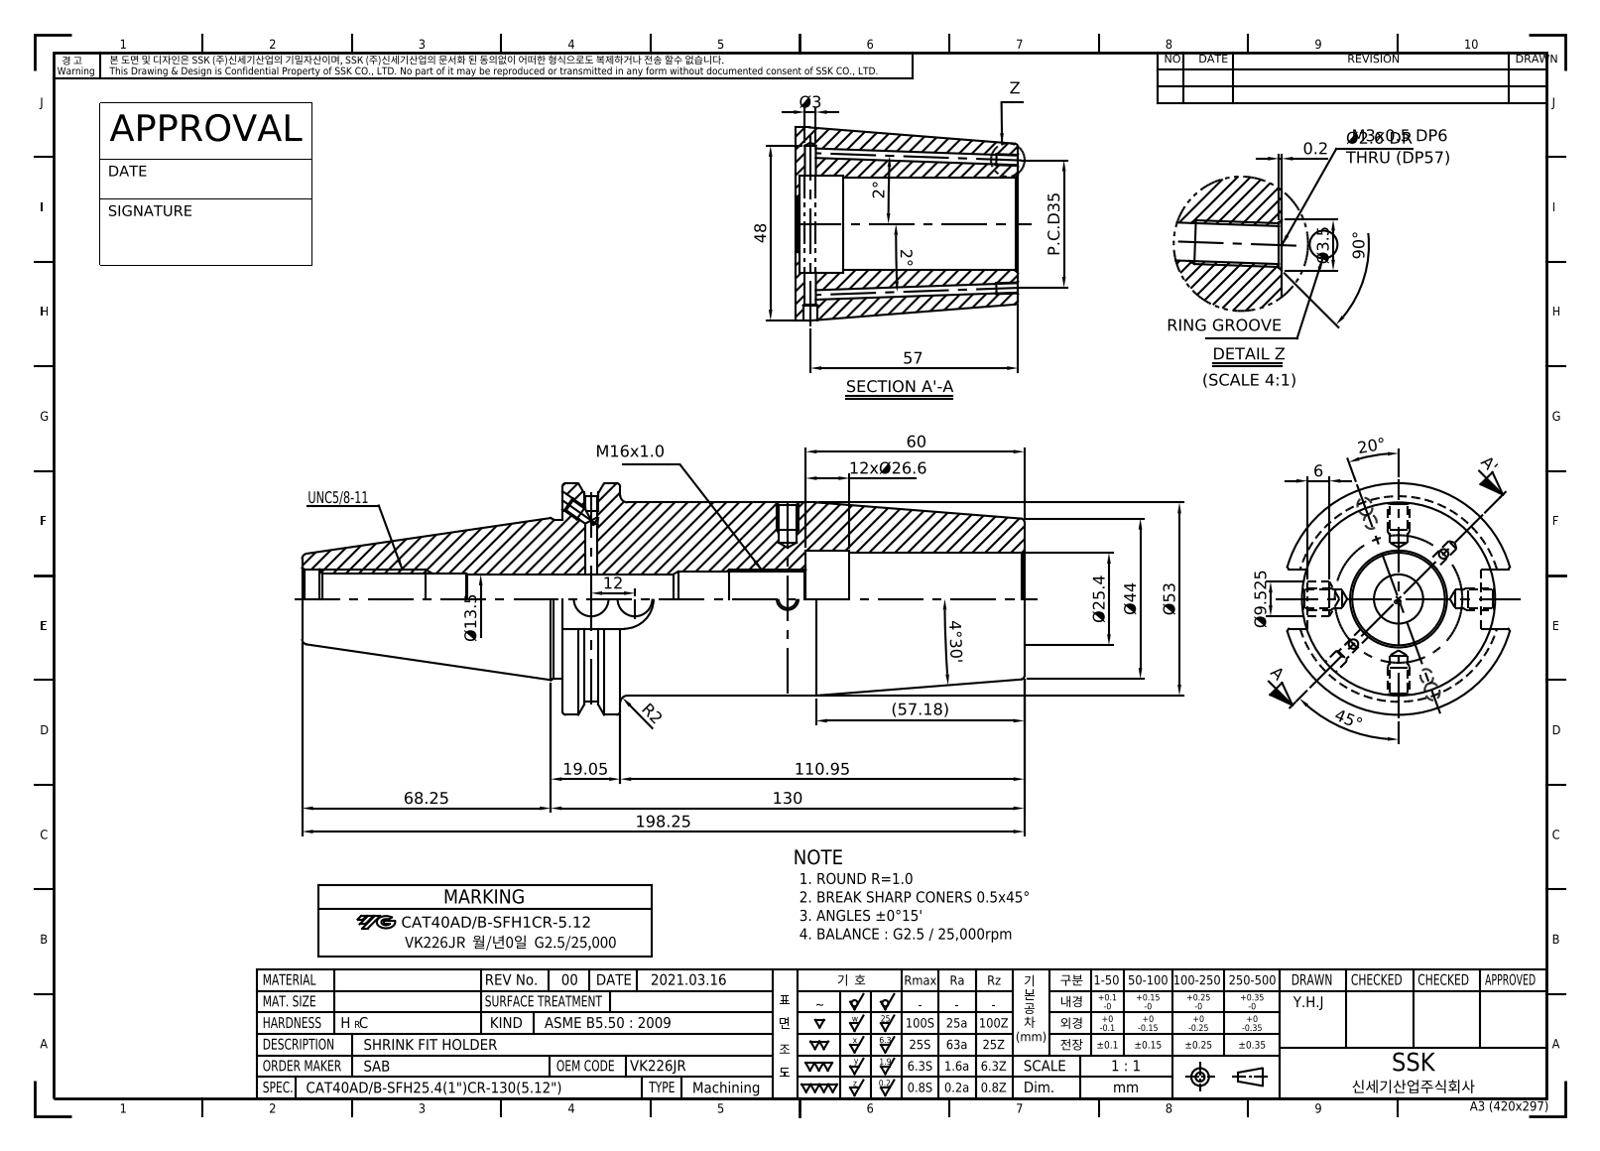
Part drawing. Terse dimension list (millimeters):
name: LO-CAT40ADB-SFH25.4CR-130
written by: Autodesk Inventor 2022 (AUTOMOTIVE_DESIGN)
unit: mm
bodies: 1 solid, 91 faces (34 planar, 33 cylindrical, 24 other)
size: 198.25 × 63.5 × 61.09
volume: 284 993 mm³; area: 45 781 mm²
holes: 4× ⌀3.24, 2× ⌀2.46, 2× ⌀4, 2× ⌀4.2, 1× ⌀9.53, 1× ⌀13, 1× ⌀13.39, 1× ⌀14.92, 1× ⌀16.3, 1× ⌀25.4, 1× ⌀26.6
bosses: 1× ⌀63.5, 1× ⌀53, 1× ⌀43.6
rounds: 1× R8.19, 1× R28.15
face distances: 126.83, 66.83, 60, 15.88, 50.95, 110.95, 47.6, 16.38, 71.42, 87.3
